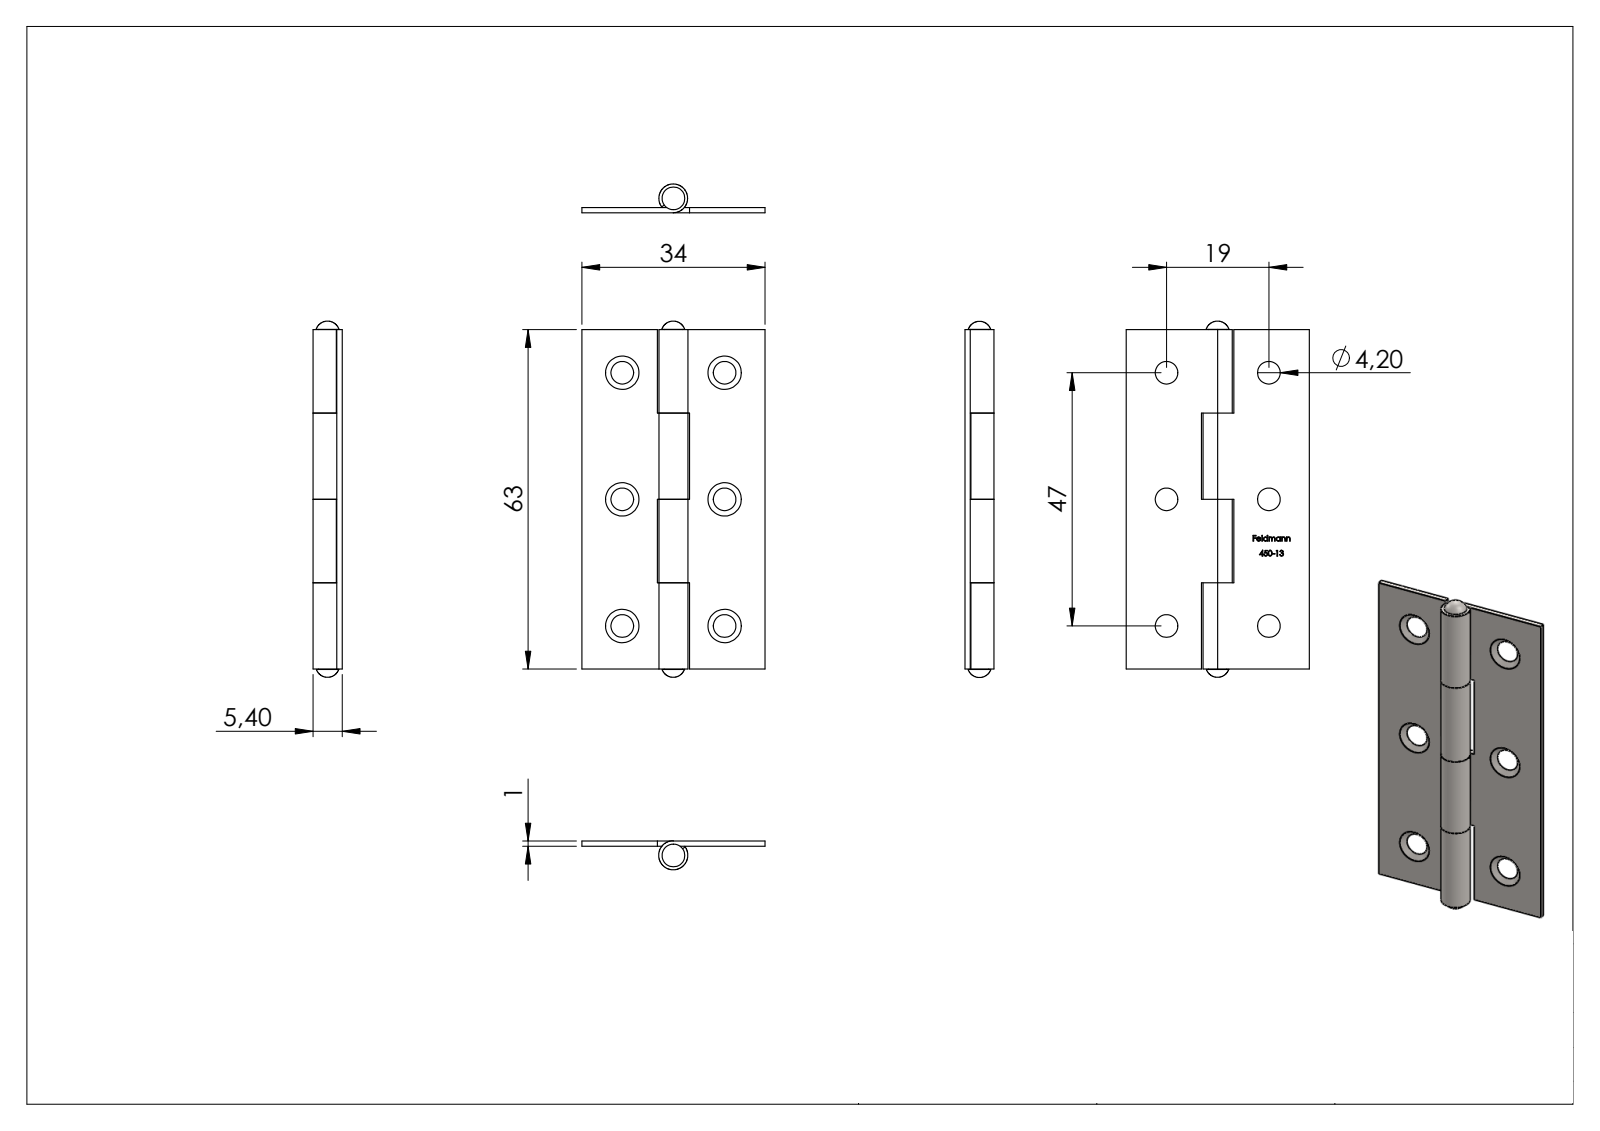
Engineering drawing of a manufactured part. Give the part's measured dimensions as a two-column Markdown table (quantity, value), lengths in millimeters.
| quantity | value |
| --- | --- |
| part name | 450-13 Teil1; 450-13 Teil3; 450-13 Teil2; 450-13 |
| STEP written by | SolidWorks 2018 (CONFIG_CONTROL_DESIGN) |
| units | millimeters |
| bodies | 3 solids, 227 faces (131 planar, 9 cylindrical, 87 other) |
| overall size | 66.1 × 34 × 5.4 |
| volume | 3 162 mm³ |
| surface area | 6 420 mm² |
| round holes (diameter × count) | 3.4 × 1 |
| round bosses / shafts (diameter × count) | 5.4 × 1 |
| main face-to-face distances | 1, 31.5, 14, 20, 34, 16, 15.5, 63, 6, 47.5 |
